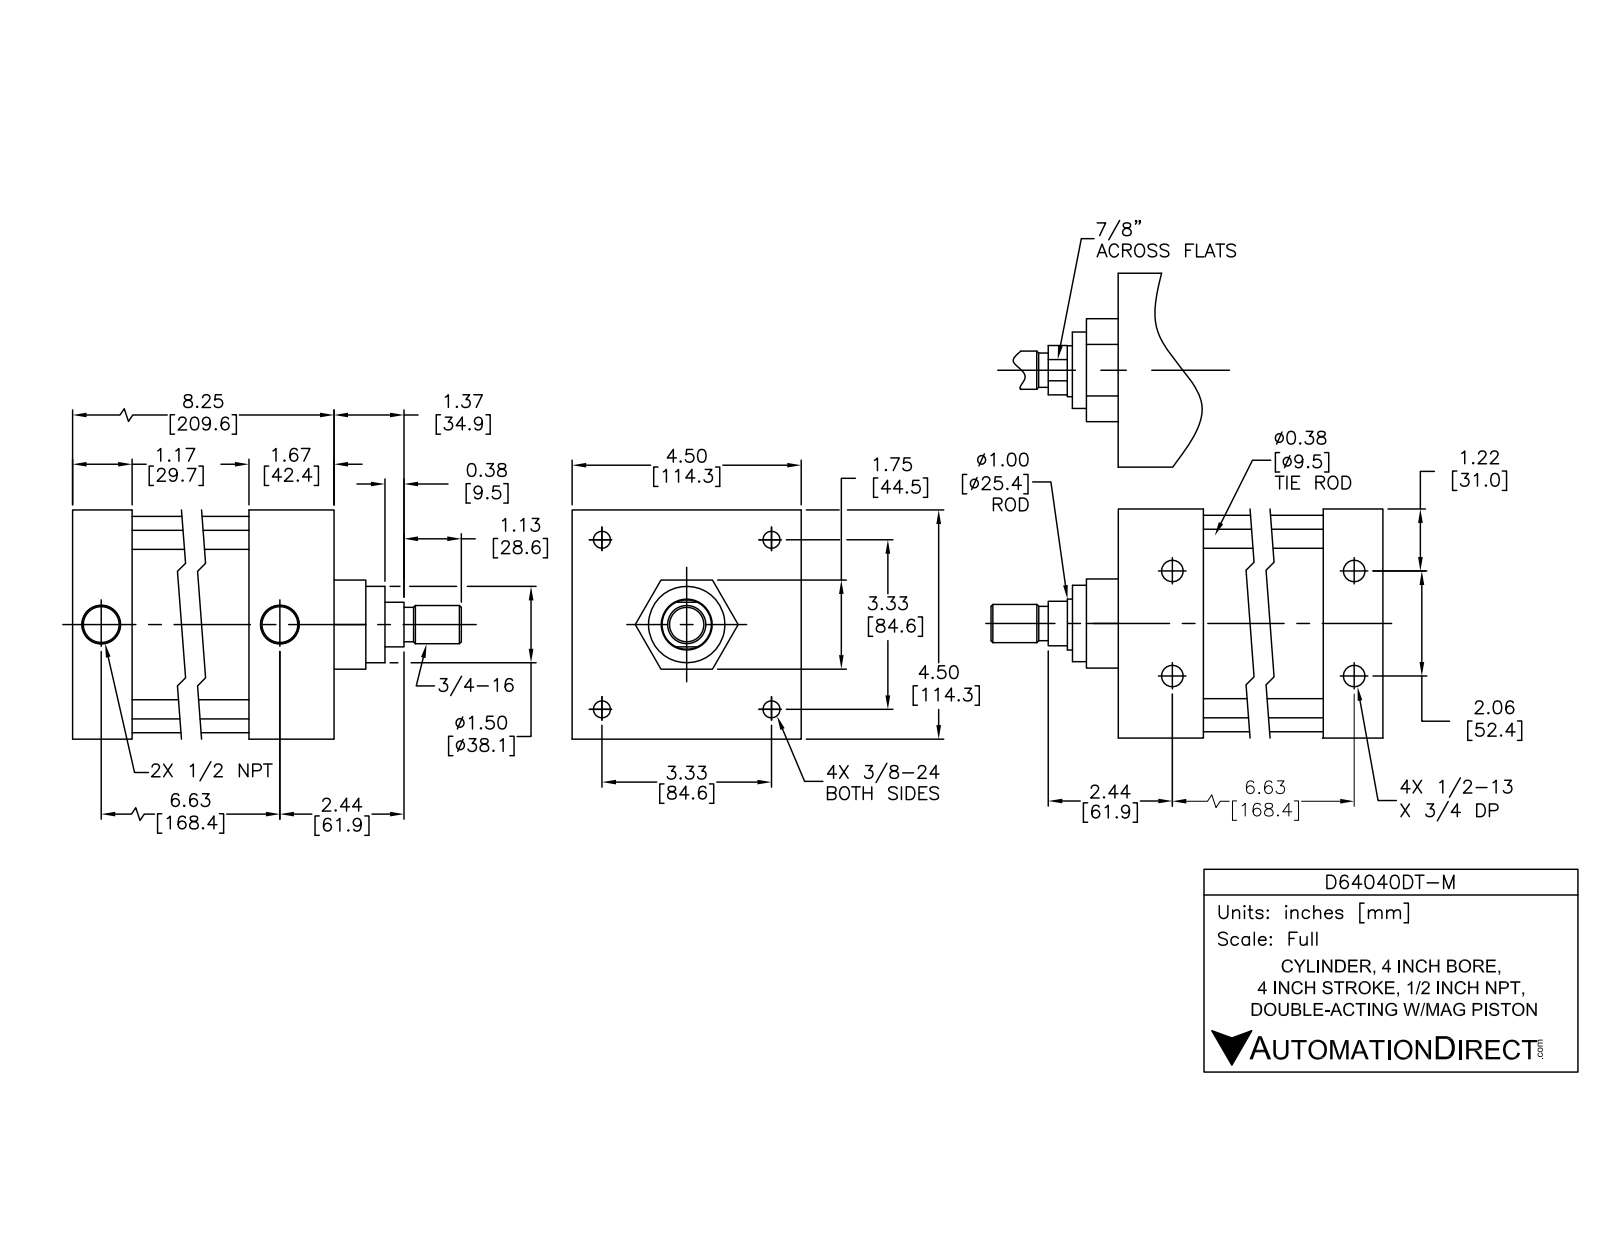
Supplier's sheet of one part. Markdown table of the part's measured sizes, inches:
| quantity | value |
| --- | --- |
| part name | D64040DT-M BODY; D64040DT-M PISTON; D64040DT-M |
| STEP written by | SolidWorks 2015 (AUTOMOTIVE_DESIGN) |
| units | inches |
| bodies | 12 solids, 303 faces (99 planar, 114 cylindrical, 90 other) |
| overall size | 10.745 × 4.5 × 4.5 |
| volume | 88.4 in³ |
| surface area | 423.7 in² |
| round holes (diameter × count) | 0.33 × 4, 0.406 × 4, 0.417 × 4, 0.625 × 4, 0.5 × 2, 0.766 × 2, 1 × 1, 1.003 × 1, 4 × 1 |
| round bosses / shafts (diameter × count) | 0.609 × 4, 0.375 × 4, 0.34 × 4, 4.25 × 1, 3.997 × 1, 1.75 × 1, 0.997 × 1, 0.97 × 1 |
| partial cylindrical surfaces (radius × count) | 0.45 × 4 |
| main face-to-face distances | 4.5, 0.08, 5.326, 8.246, 1.75, 6.997, 1.249, 5.751, 1.246, 2.495 |
| hole center spacings | 3.322, 6.702, 6.622, 1.031, 1.031, 2.062, 2.349, 4.698 |
